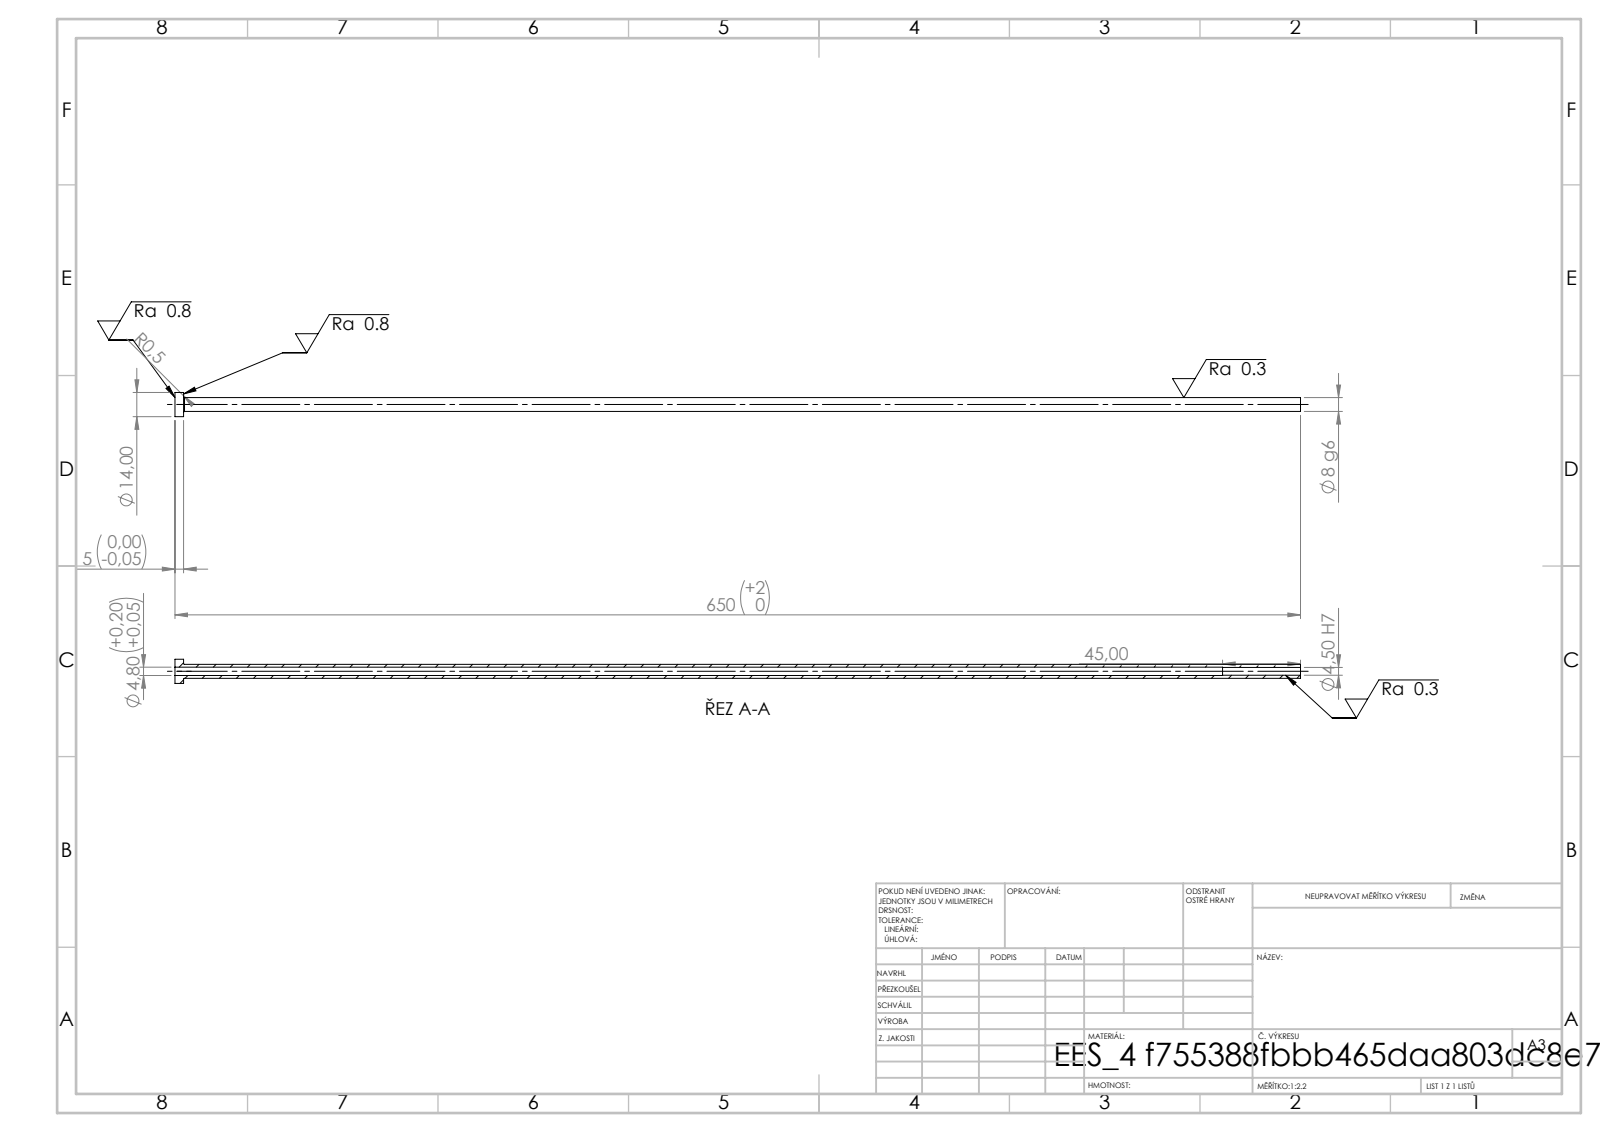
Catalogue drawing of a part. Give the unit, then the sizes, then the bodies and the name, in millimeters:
Units: millimetres
Overall size (bounding box): 650 × 14 × 14
Round holes (diameter × count): ⌀4.5 ×1, ⌀4.8 ×1
Round bosses / shafts (diameter × count): ⌀14 ×1, ⌀8 ×1
Main face-to-face distances: 5, 650, 645, 605, 600, 45
Volume: 21 529 mm³ · Surface area: 26 461 mm²
Bodies: 1 solid, 14 faces (4 planar, 8 cylindrical, 2 other)
STEP written by: SolidWorks 2019 (CONFIG_CONTROL_DESIGN)
